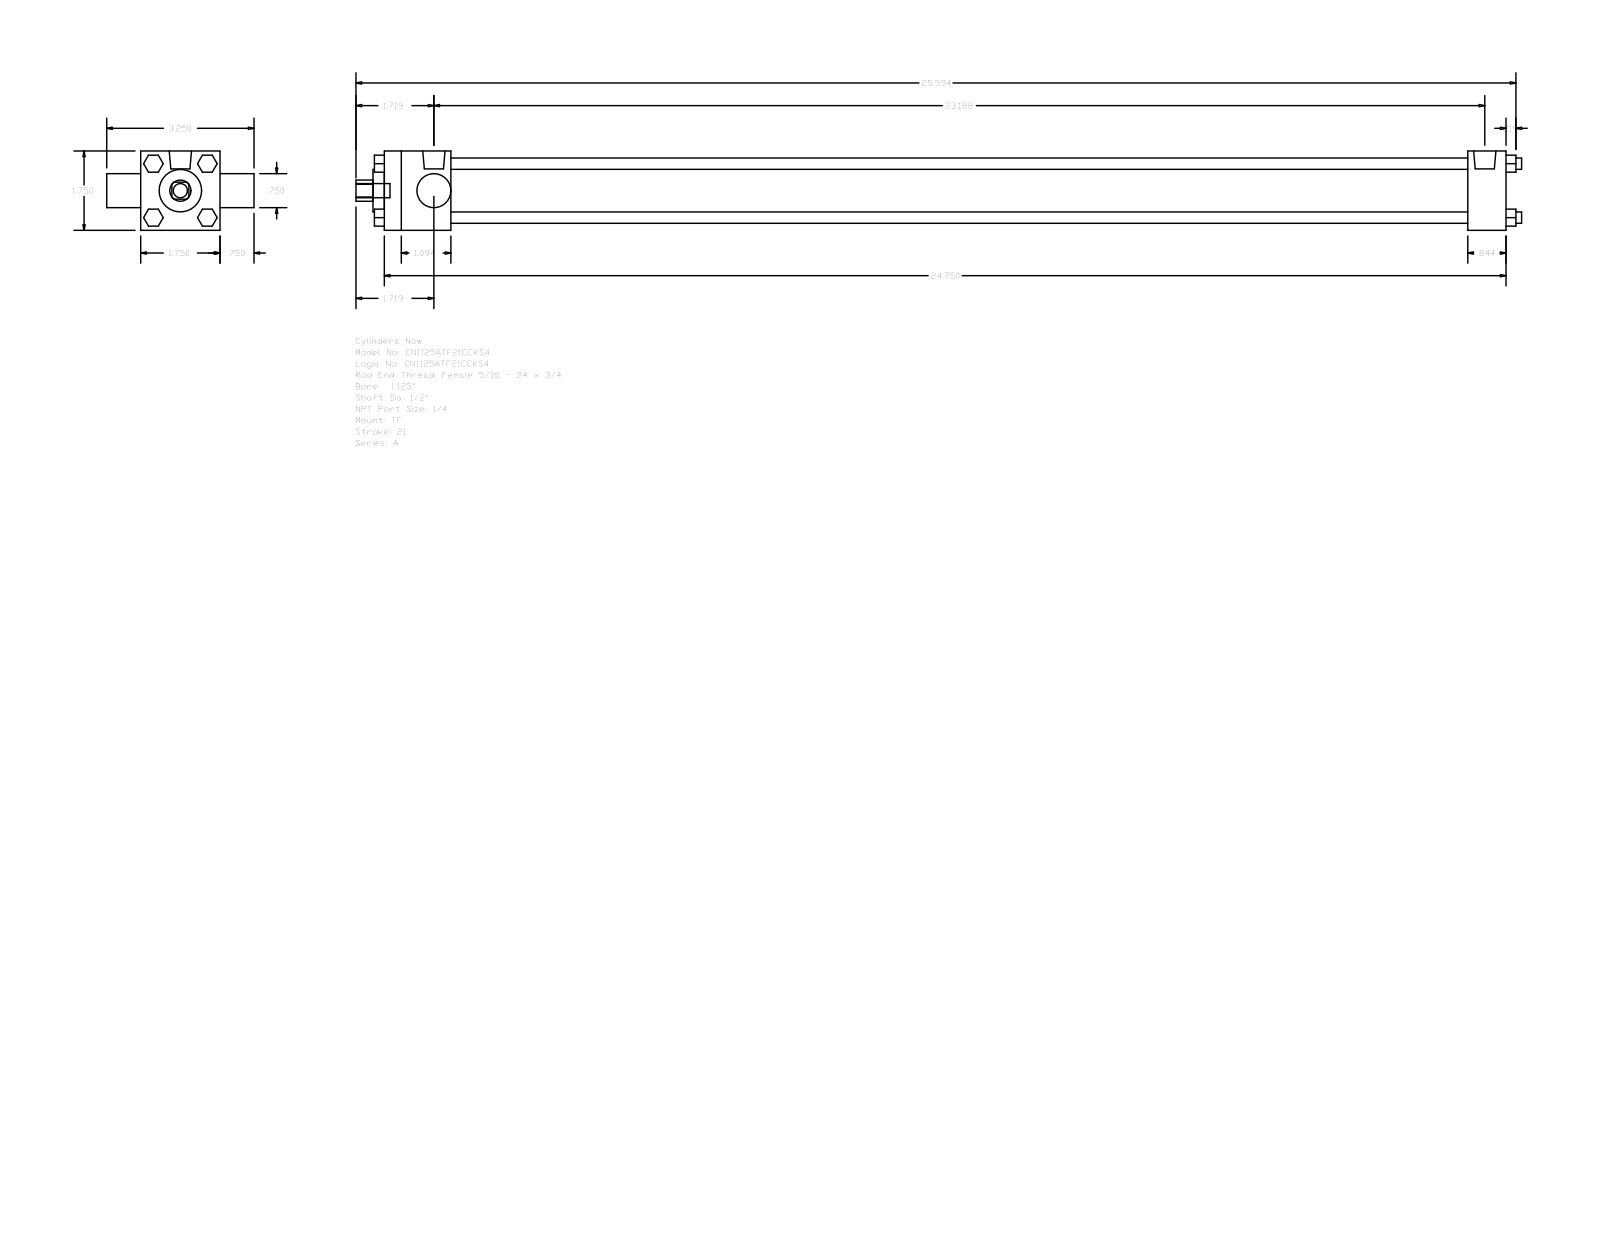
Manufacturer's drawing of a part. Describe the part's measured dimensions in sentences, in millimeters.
The part is named "A_TF__0112_0.5". Its 3-D file was written by "GSSL Pune (CONFIG_CONTROL_DESIGN)". It is 0 solids with 120 faces: 92 planar, 28 cylindrical and 0 other. Overall it measures 653.26 by 82.55 by 44.45 millimeters. Round holes: 1 of diameter 12.7, 1 of diameter 19.05, 1 of diameter 23.81, 1 of diameter 31.88. Round bosses or shafts: 4 of diameter 6.35, 3 of diameter 5.56, 2 of diameter 12.49, 1 of diameter 7.94. Partial cylindrical surfaces (rounded edges, fillets, slot ends): 1 of radius 5.94. The main face-to-face distances are 44.46, 628.64, 607.21, 21.43, 37.3, 569.91, 591.34, 19.04, 63.5, 9.53.
